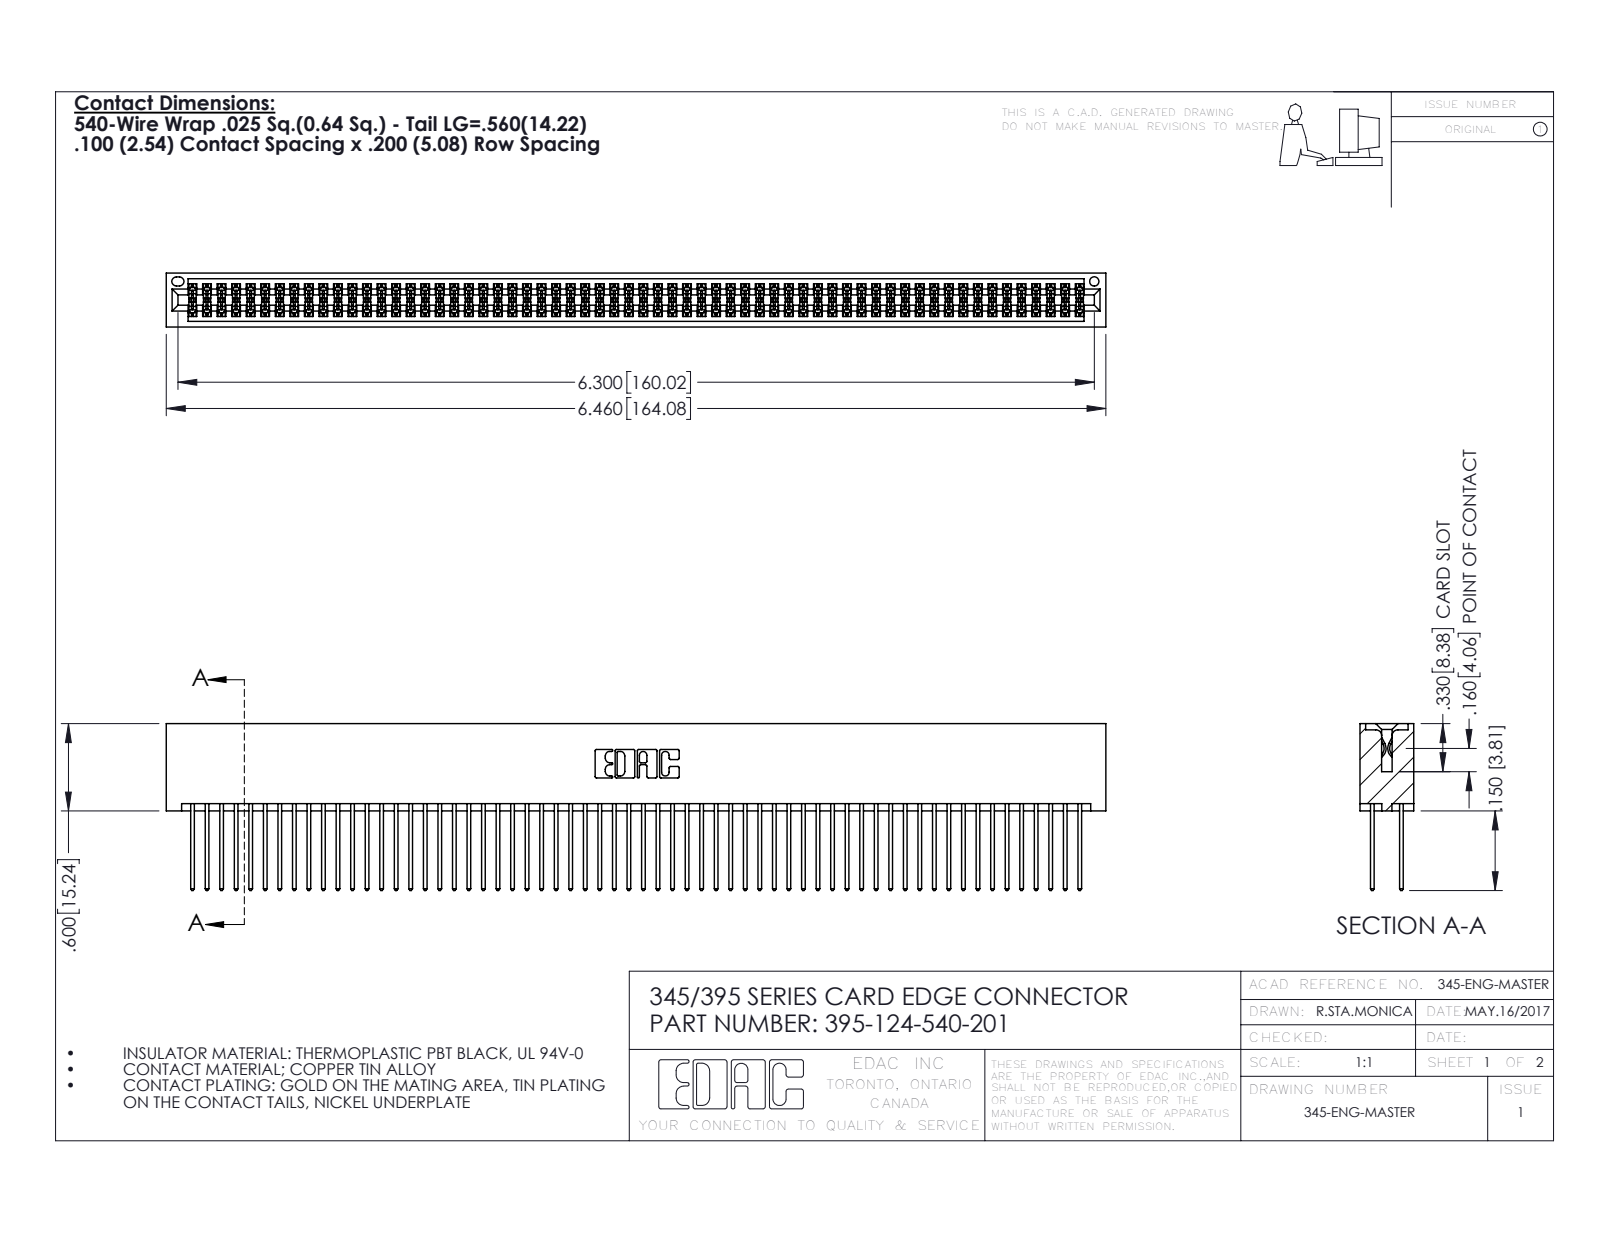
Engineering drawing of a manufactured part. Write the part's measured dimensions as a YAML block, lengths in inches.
part_name: "345-292-001_345-293-140; 395-124-540-201; 345 Part_No Mounting Lugs"
step_written_by: "SolidWorks 2016 (CONFIG_CONTROL_DESIGN)"
units: inches
bodies: {solids: 125, faces: 6318, planar: 4168, cylindrical: 2150, other: 0}
overall_size: [6.46, 1.147, 0.37]
volume: 1.05
surface_area: 43.88
round_holes:
  - {diameter: 0.064, count: 1}
partial_cylinders:
  - {radius: 0.006, count: 186}
  - {radius: 0.01, count: 124}
  - {radius: 0.01, count: 22}
  - {radius: 0.007, count: 6}
  - {radius: 0.031, count: 6}
  - {radius: 0.026, count: 3}
  - {radius: 0.014, count: 2}
  - {radius: 0.019, count: 2}
face_to_face_distances: [0.298, 0.072, 0.2, 0.098, 0.272, 0.025, 0.225, 0.37, 0.175, 0.149]
